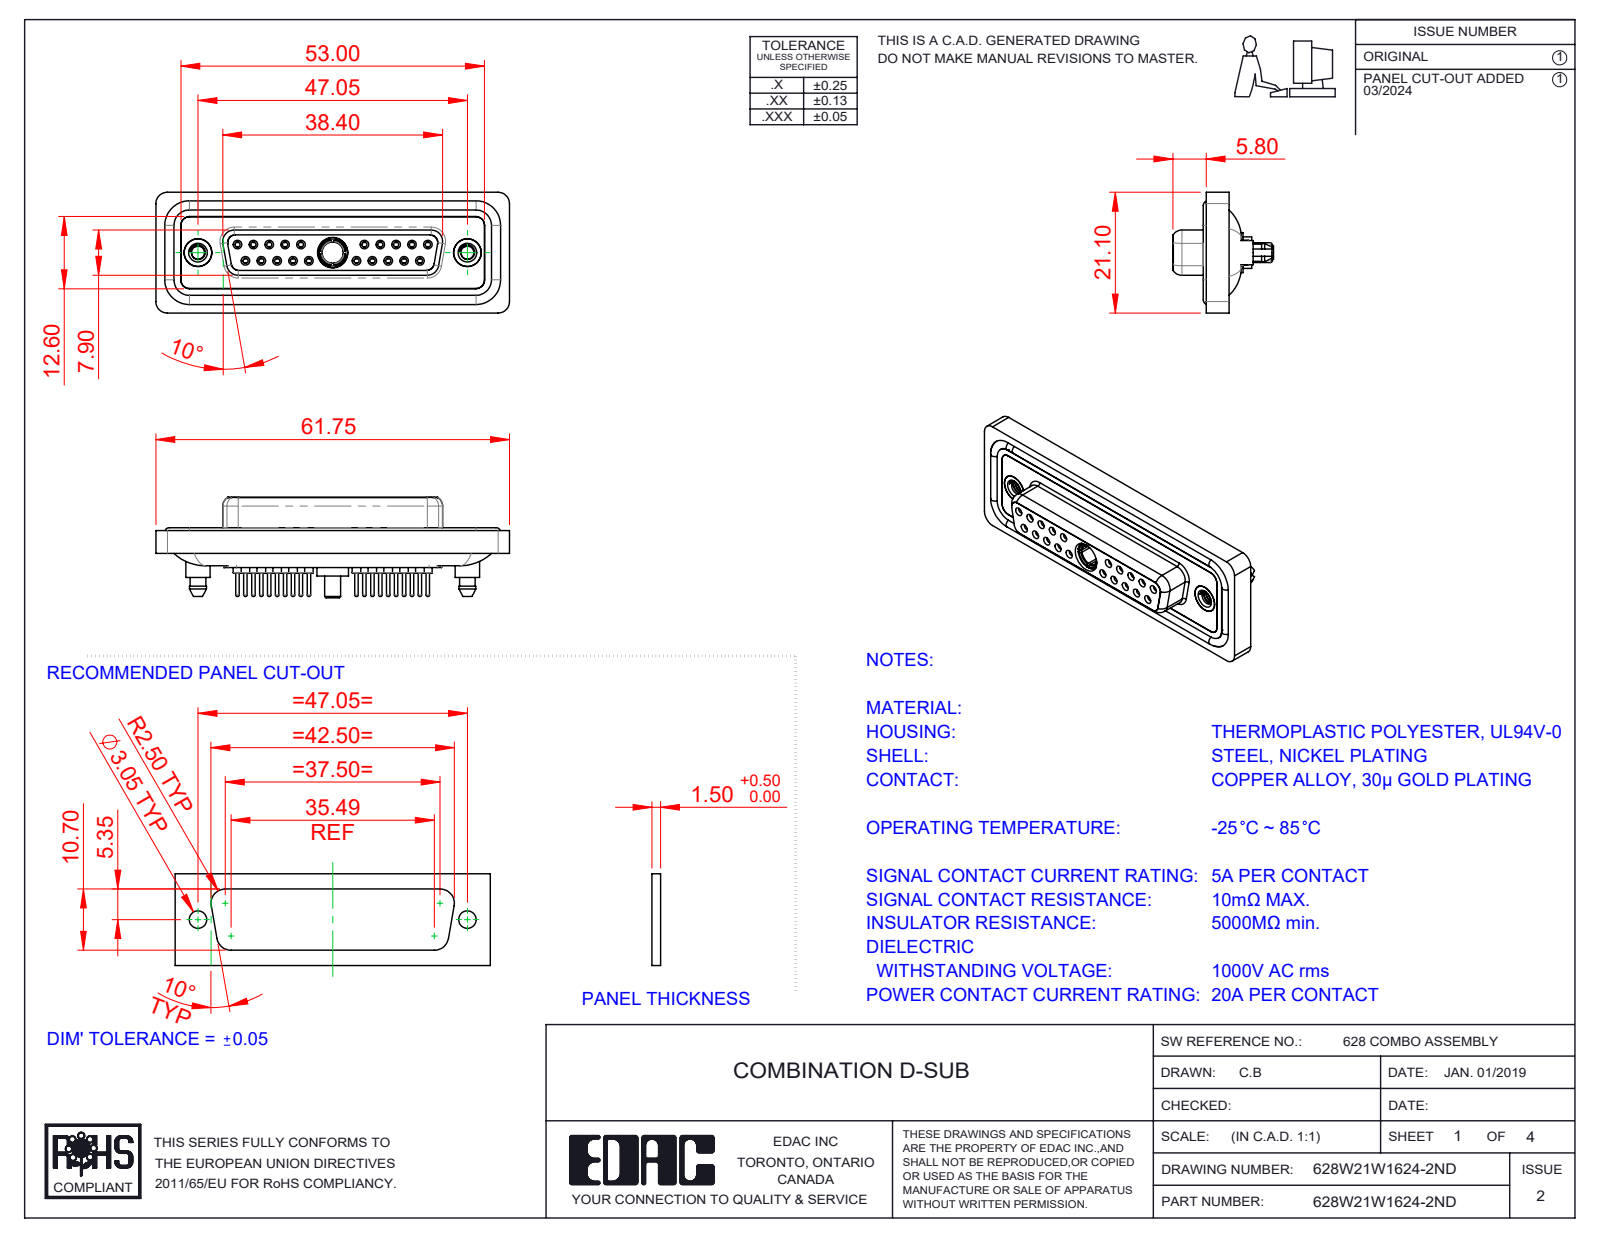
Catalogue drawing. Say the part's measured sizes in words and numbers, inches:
The part is named "628Combo Housing_21W1; 628W21W1624-2ND; 628Combo Contact Row 1_24; 628Combo Threaded Boardlock_D (+5 more)". Its 3-D file was written by "SolidWorks 2023 (CONFIG_CONTROL_DESIGN)". It is 29 solids with 1626 faces: 450 planar, 639 cylindrical and 537 other. Overall it measures 2.431 by 0.831 by 0.691 inches. Its volume is 0.519 cubic inches and its surface area 22.23 square inches. Round holes: 20 of diameter 0.035, 20 of diameter 0.043, 20 of diameter 0.059, 20 of diameter 0.079, 10 of diameter 0.063, 10 of diameter 0.067, 3 of diameter 0.191, 2 of diameter 0.089, 2 of diameter 0.157, 2 of diameter 0.159, 2 of diameter 0.197, 1 of diameter 0.146. Round bosses or shafts: 20 of diameter 0.087, 20 of diameter 0.024, 14 of diameter 0.063, 2 of diameter 0.213, 2 of diameter 0.195, 2 of diameter 0.189, 2 of diameter 0.167, 1 of diameter 0.217. Partial cylindrical surfaces (rounded edges, fillets, slot ends): 24 of radius 0.059, 18 of radius 0.079, 10 of radius 0.063, 8 of radius 0.053, 4 of radius 0.01, 4 of radius 0.02, 4 of radius 0.024, 4 of radius 0.026. The main face-to-face distances are 0.016, 0.071, 0.293, 0.26, 0.222, 0.063, 0.02, 0.278, 0.114, 0.043. The hole center spacings are 0.124, 0.109, 0.218, 0.198, 0.327, 0.294, 0.654, 0.763.
